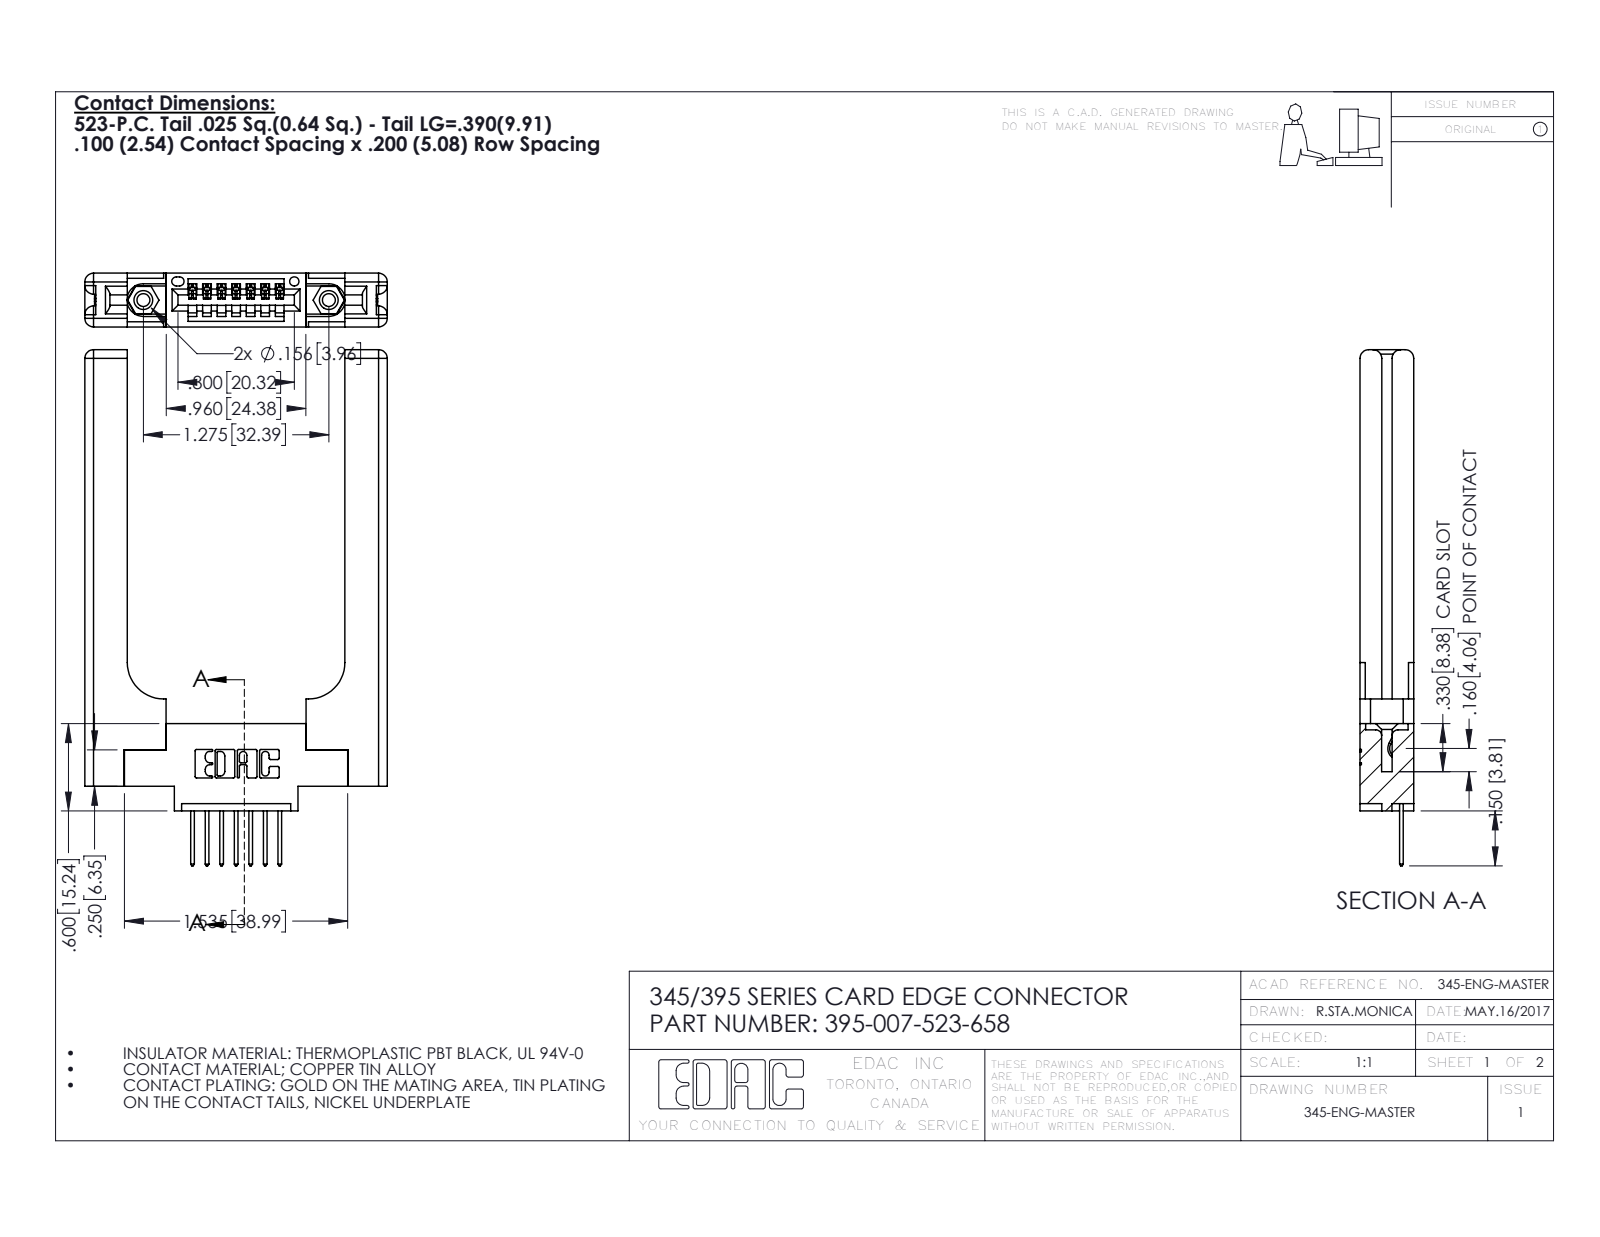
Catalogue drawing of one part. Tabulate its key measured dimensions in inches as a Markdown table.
| quantity | value |
| --- | --- |
| part name | 345-250-001_345-250-001-102; 395-007-523-658; 345-220-058_345-220-058; 345 Part_0.170 Offset - 0.156 Dia-TH (+1 more) |
| STEP written by | SolidWorks 2016 (CONFIG_CONTROL_DESIGN) |
| units | inches |
| bodies | 12 solids, 792 faces (512 planar, 220 cylindrical, 60 other) |
| overall size | 3.547 × 2.079 × 0.37 |
| volume | 0.8 in³ |
| surface area | 17.2 in² |
| round holes (diameter × count) | 0.089 × 2, 0.125 × 2, 0.156 × 2, 0.064 × 1 |
| round bosses / shafts (diameter × count) | 0.155 × 2 |
| partial cylindrical surfaces (radius × count) | 0.01 × 22, 0.06 × 16, 0.006 × 14, 0.01 × 14, 0.007 × 6, 0.031 × 6, 0.026 × 3, 0.03 × 2 |
| main face-to-face distances | 0.37, 0.15, 0.22, 0.072, 0.077, 0.148, 0.298, 1.496, 0.071, 0.12 |
| hole center spacings | 0.27, 1.045, 1.275 |
